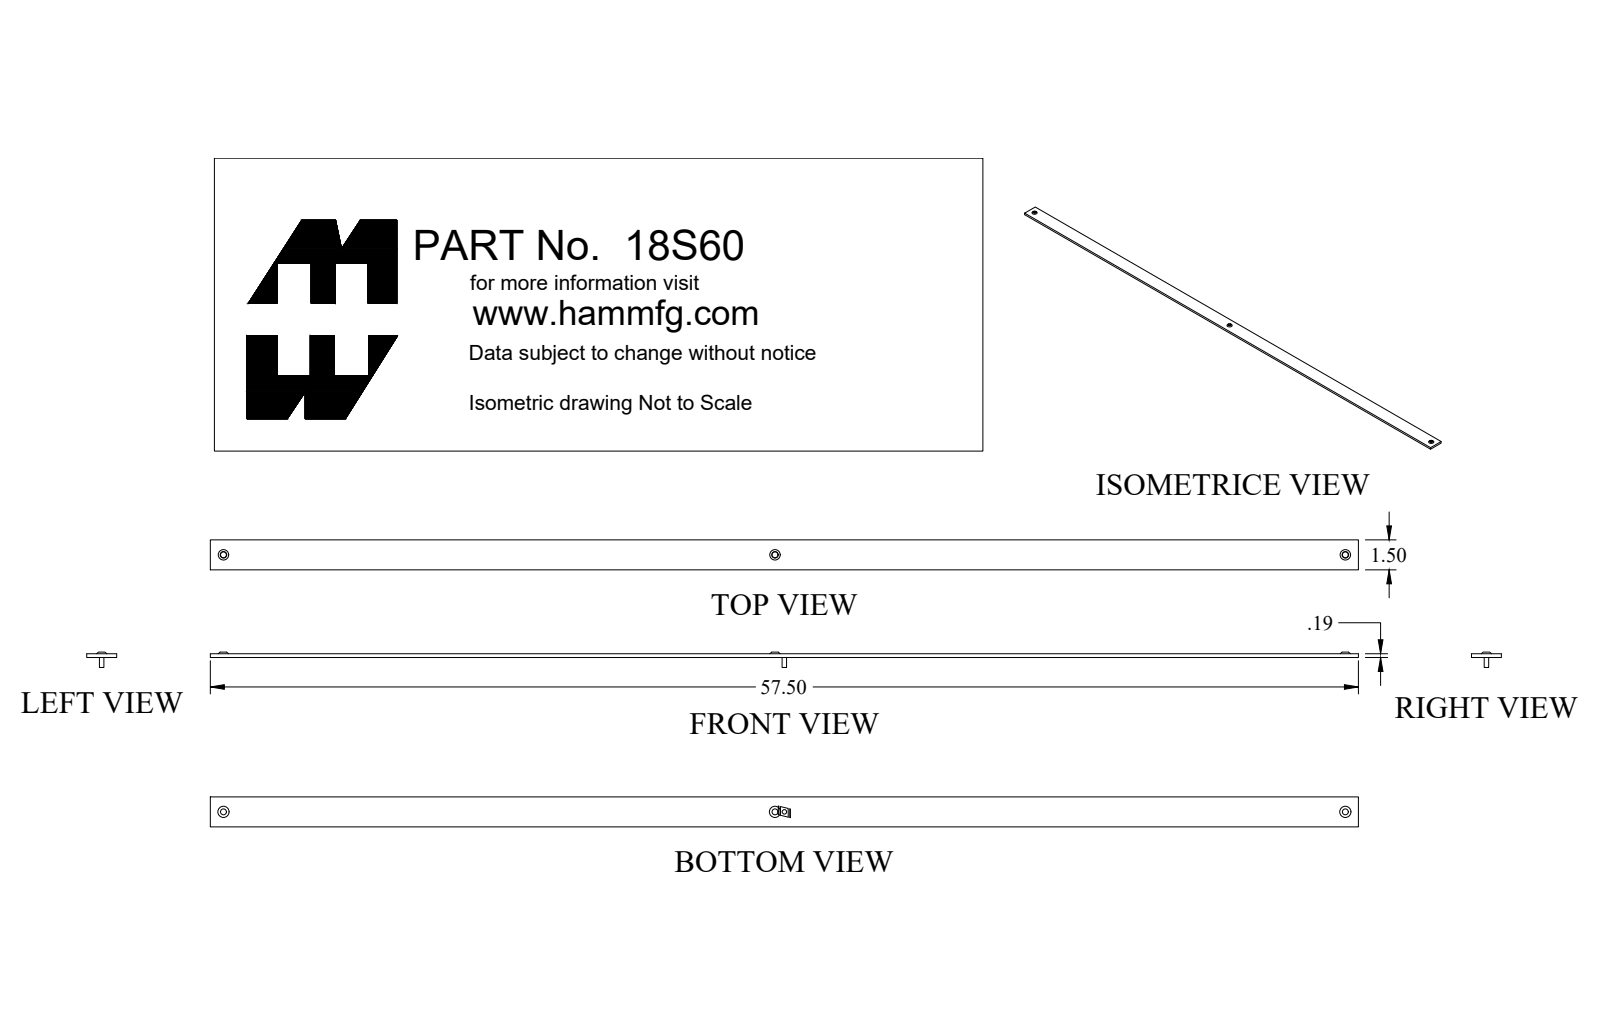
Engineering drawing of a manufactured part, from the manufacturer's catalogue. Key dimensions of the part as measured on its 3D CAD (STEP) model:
Part name (STEP PRODUCT): 18S60_Default
STEP written by: SolidWorks 2018 (CONFIG_CONTROL_DESIGN)
Units: inches
Bodies: 1 solid, 27 faces (9 planar, 6 cylindrical, 12 other)
Overall size (bounding box): 57.5 × 1.5 × 0.27
Volume: 16.16 in³ · Surface area: 195 in²
Round holes (diameter × count): ⌀0.296 ×3
Main face-to-face distances: 0.188, 1.5, 57.5, 0.27, 0.082
Hole centre spacings: 27.625, 28.563, 56.188
